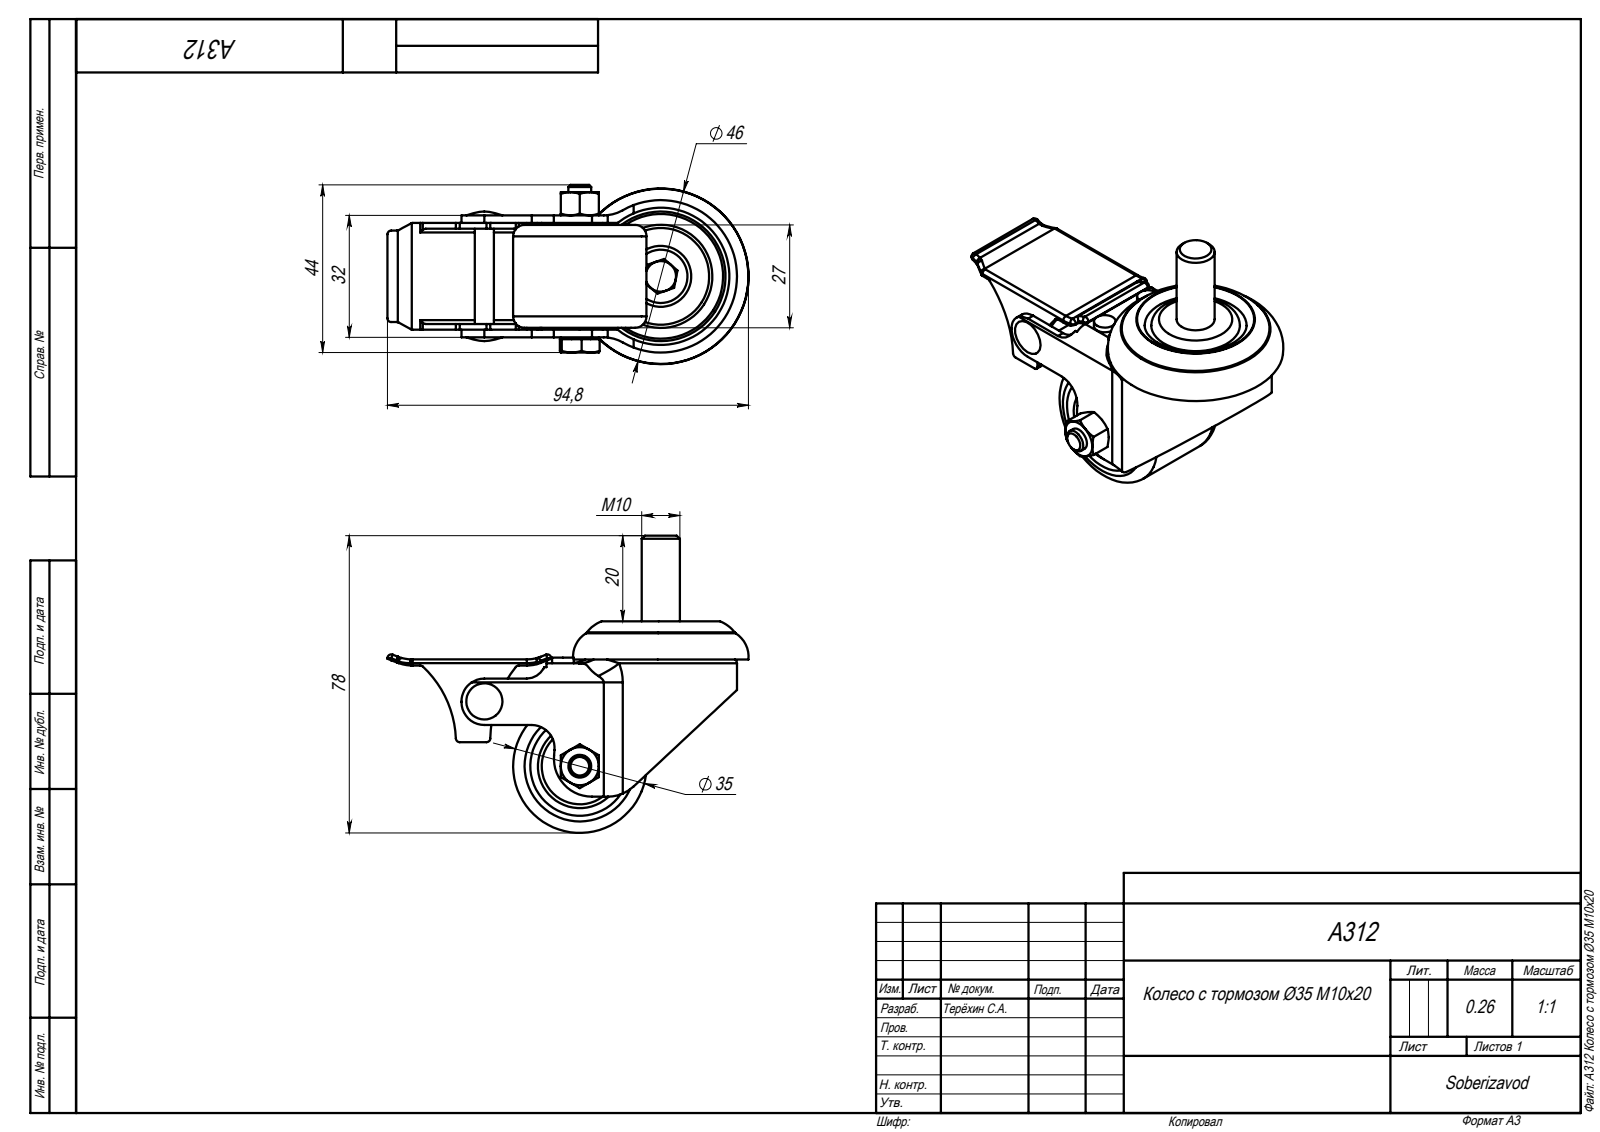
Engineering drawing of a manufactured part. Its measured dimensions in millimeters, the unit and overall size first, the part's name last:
Units: millimetres
Overall size (bounding box): 94.79 × 77.99 × 47.04
Round holes (diameter × count): ⌀5 ×2, ⌀10 ×2, ⌀6 ×1, ⌀12 ×1, ⌀22 ×1
Round bosses / shafts (diameter × count): ⌀5.7 ×2, ⌀35 ×1, ⌀20 ×1, ⌀16 ×1
Partial cylindrical surfaces — rounded edges, fillets, slot ends (radius × count): R1 ×27, R10 ×8, R5 ×5, R6 ×3, R18 ×1, R20 ×1, R27.38 ×1, R31.26 ×1
Main face-to-face distances: 2, 28, 30, 4, 1.5, 26, 1.03, 0.5, 0.58, 1.61
Hole centre spacings: 30.28
Volume: 50 211 mm³ · Surface area: 32 213 mm²
Bodies: 11 solids, 317 faces (98 planar, 112 cylindrical, 107 other)
Part name (STEP PRODUCT): Дно_00; hex nut gradec_din_Hexagon Nut ISO 4034 - M6 - N; Защита_00; Крышка_00 (+6 more)
STEP written by: SolidWorks 2018 (AUTOMOTIVE_DESIGN)
